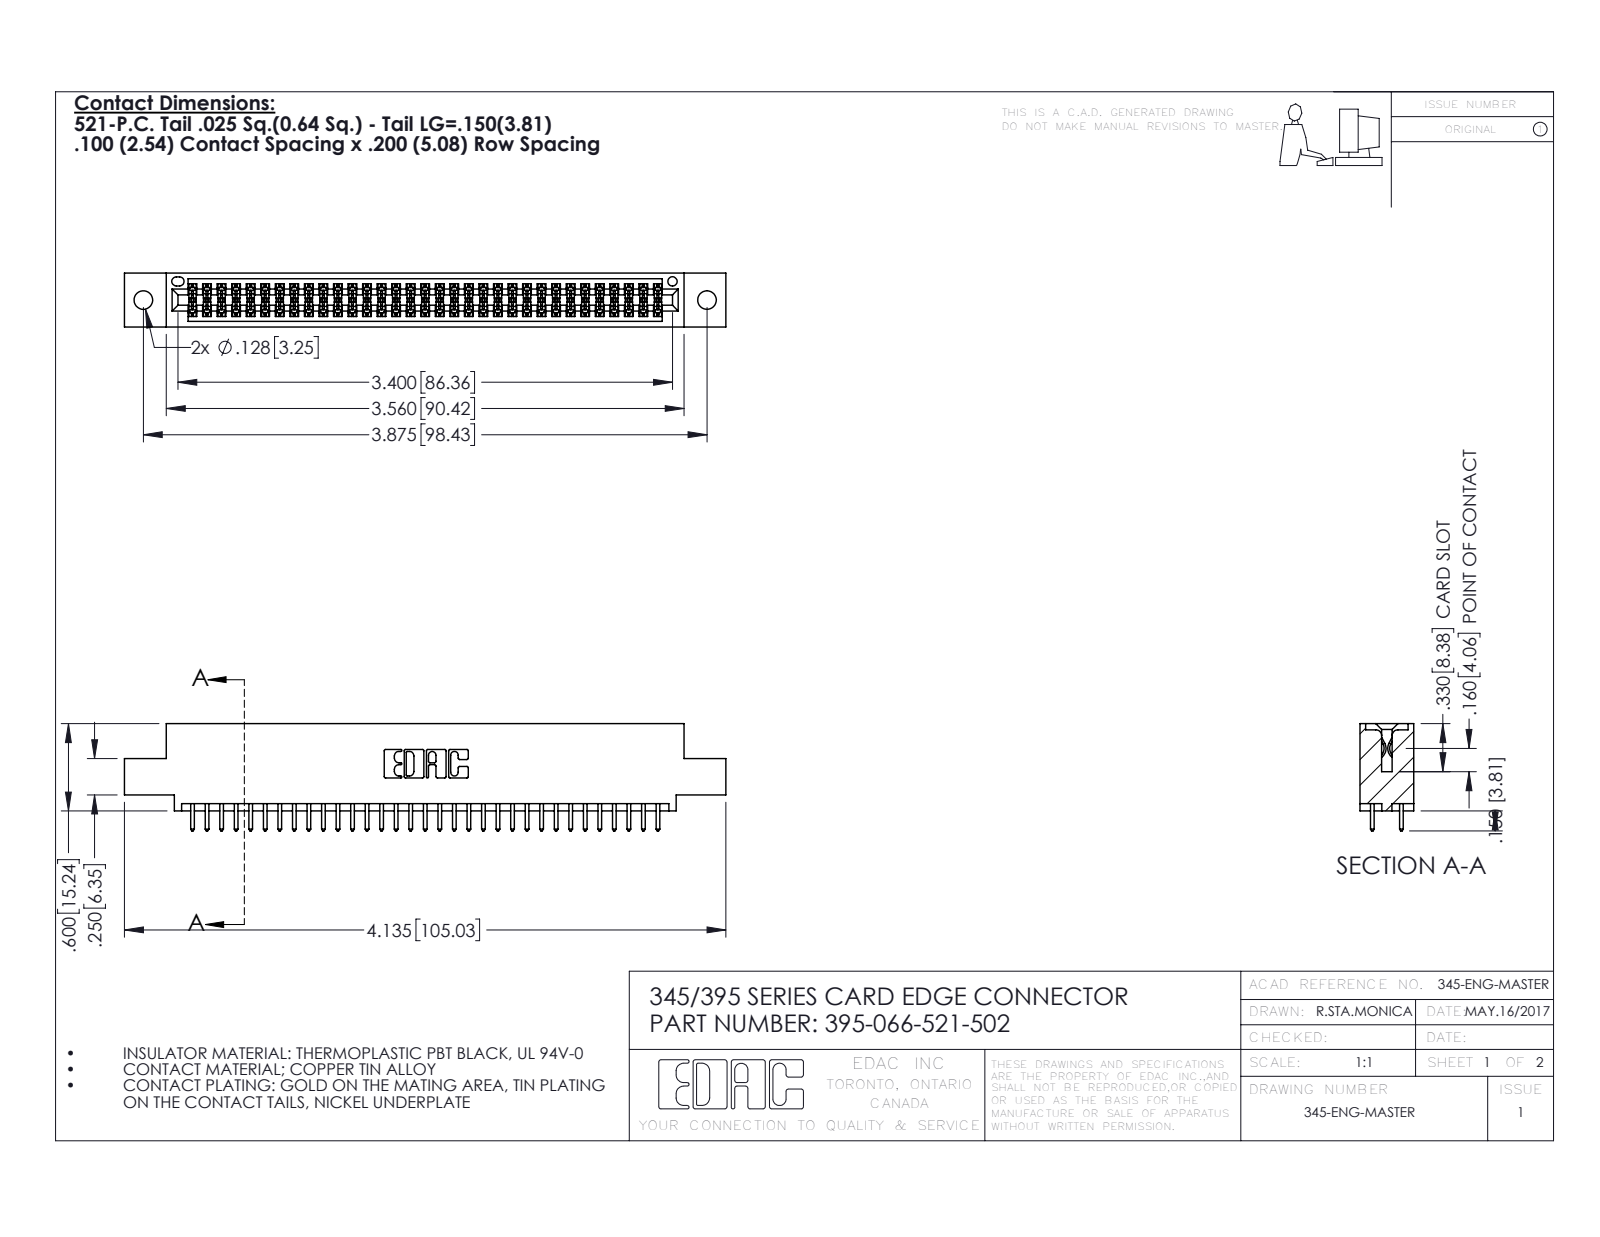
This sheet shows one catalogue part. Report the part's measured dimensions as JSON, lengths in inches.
{"part_name": "345 Part_0.110 Offset - 0.128 Dia; 345-292-001_345-293-121; 395-066-521-502", "step_written_by": "SolidWorks 2016 (CONFIG_CONTROL_DESIGN)", "units": "inches", "bodies": {"solids": 67, "faces": 3430, "planar": 2262, "cylindrical": 1168, "other": 0}, "overall_size": [4.135, 0.737, 0.37], "volume_in3": 0.609, "surface_area_in2": 22.05, "round_holes": [[0.128, 2], [0.064, 1]], "partial_cylinders_radius": [[0.006, 99], [0.01, 66], [0.01, 22], [0.007, 6], [0.031, 6], [0.026, 3], [0.014, 2], [0.019, 2]], "face_to_face_distances": [0.298, 0.072, 0.2, 0.37, 0.098, 0.272, 0.025, 0.225, 0.175, 0.149], "hole_center_spacings": [0.27, 3.64, 3.875]}
